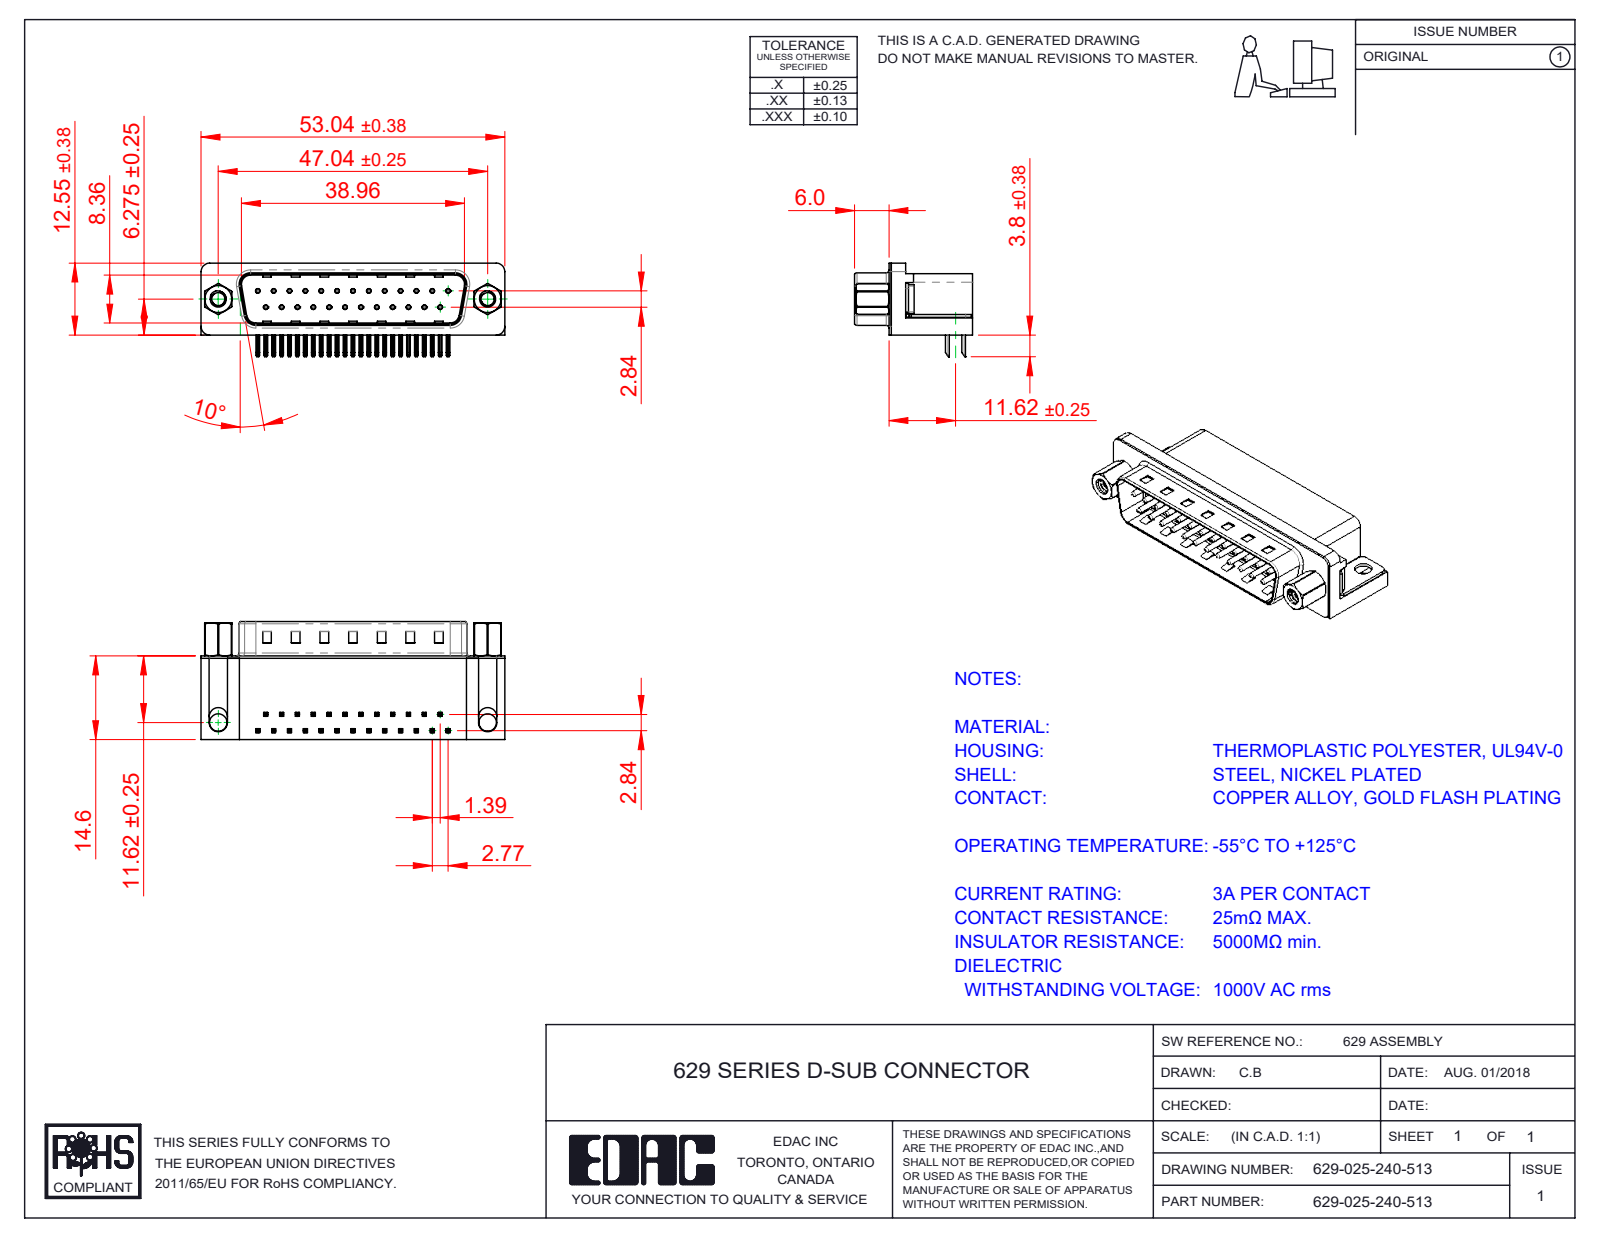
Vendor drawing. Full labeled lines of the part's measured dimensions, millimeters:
Part name (STEP PRODUCT): 629 4-40 Threaded Rivet; 629 Contact Top; 629-025-240-513; 629 4-40 Hex Standoff 5 (+4 more)
STEP written by: SolidWorks 2020 (CONFIG_CONTROL_DESIGN)
Units: millimetres
Bodies: 33 solids, 2387 faces (1425 planar, 731 cylindrical, 231 other)
Overall size (bounding box): 53.04 × 20.6 × 16.35
Volume: 7 535 mm³ · Surface area: 8 697 mm²
Round holes (diameter × count): ⌀0.35 ×25, ⌀0.8 ×25, ⌀2.26 ×2, ⌀2.29 ×2, ⌀3.05 ×2, ⌀4 ×2, ⌀4.8 ×2, ⌀5 ×2
Round bosses / shafts (diameter × count): ⌀0.75 ×25, ⌀4.9 ×2, ⌀4.75 ×2, ⌀3.9 ×2, ⌀2.79 ×2
Partial cylindrical surfaces — rounded edges, fillets, slot ends (radius × count): R0.25 ×108, R0.12 ×50, R1 ×16, R0.5 ×9, R1.6 ×8, R1.5 ×7, R0.9 ×4, R2 ×4
Main face-to-face distances: 0.4, 10.36, 14.2, 2.1, 8.76, 14.6, 1.7, 10.46, 10.86, 2.9
Hole centre spacings: 3.16, 2.77, 5.54, 8.31, 11.08, 13.85, 16.62, 5.03
